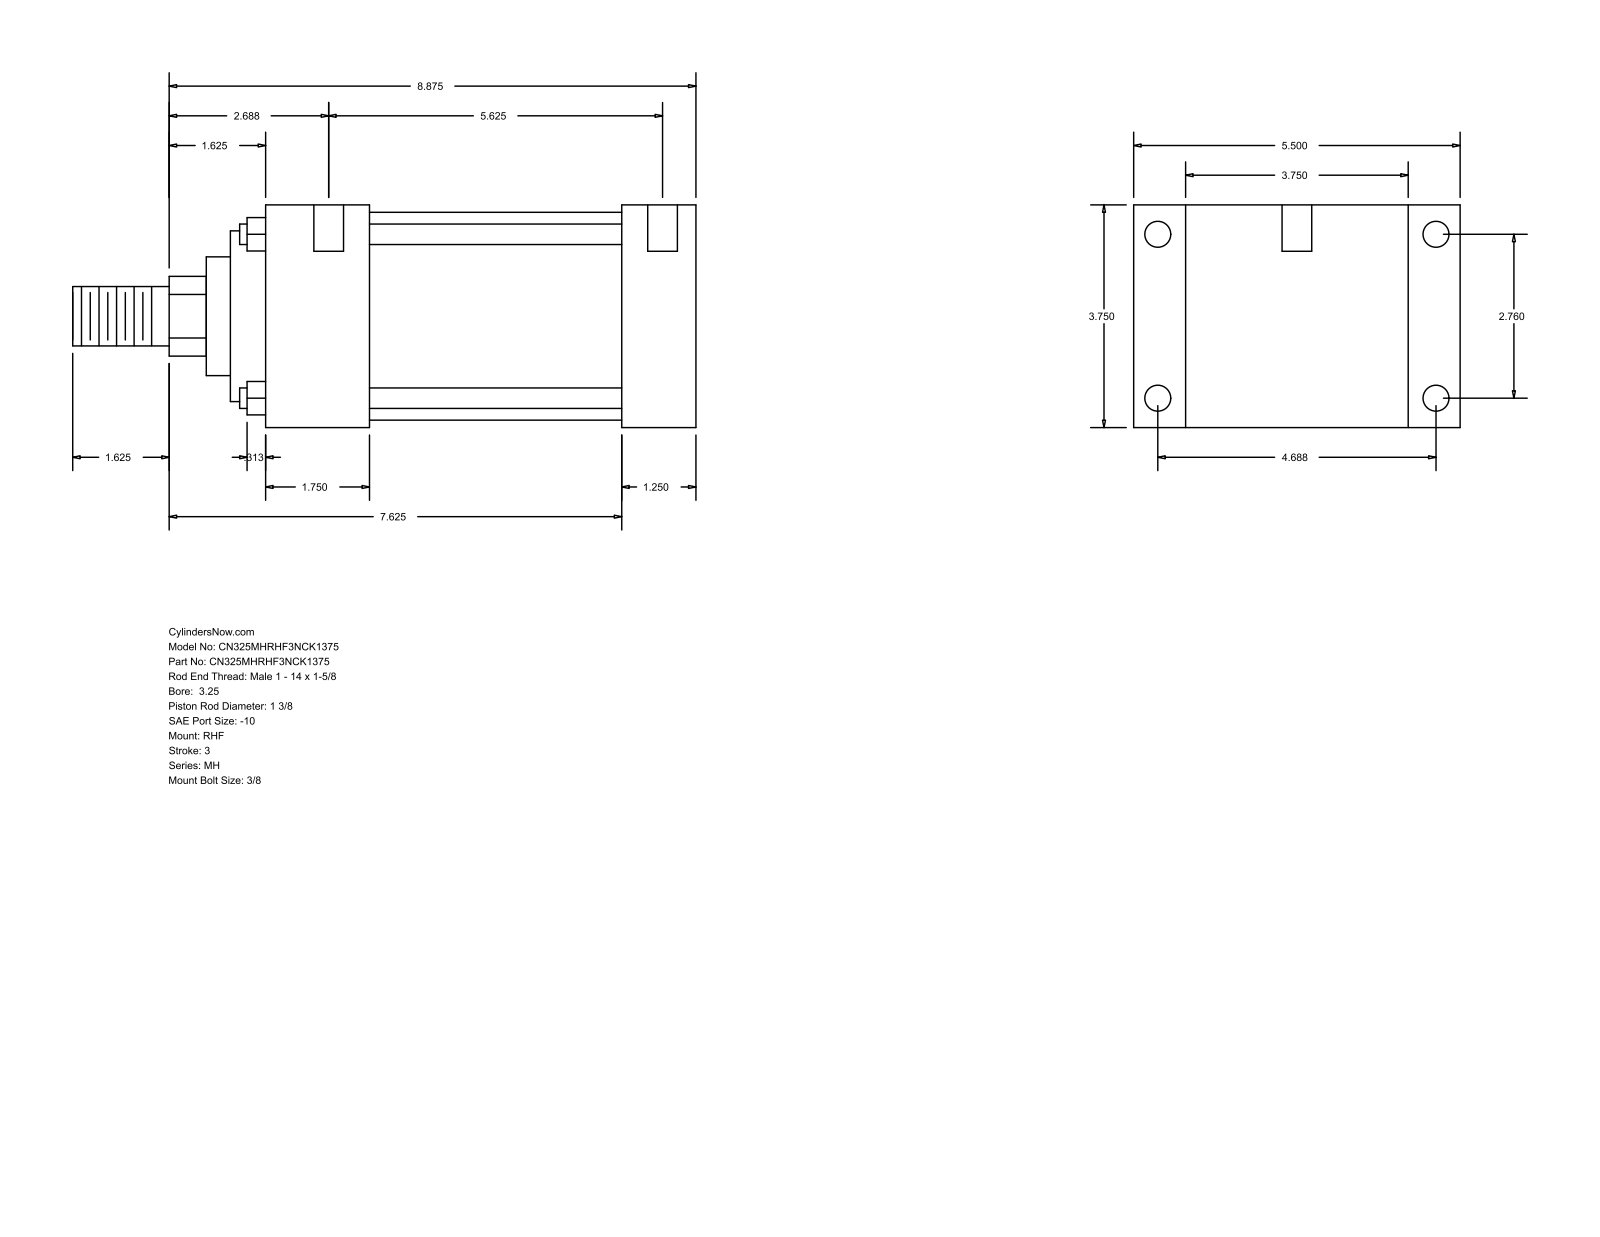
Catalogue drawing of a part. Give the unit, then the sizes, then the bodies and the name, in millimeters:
Units: millimetres
Overall size (bounding box): 266.7 × 139.7 × 95.25
Round holes (diameter × count): ⌀5.56 ×4, ⌀11.13 ×4, ⌀12.7 ×2
Round bosses / shafts (diameter × count): ⌀8.76 ×4, ⌀88.9 ×1, ⌀73.03 ×1, ⌀50.8 ×1, ⌀34.92 ×1, ⌀25.4 ×1
Partial cylindrical surfaces — rounded edges, fillets, slot ends (radius × count): R17.06 ×1
Main face-to-face distances: 95.24, 31.75, 22.23, 117.47, 152.41, 184.16, 139.7, 44.45, 107.96, 139.71
Hole centre spacings: 70.1, 119.06, 138.16, 149.23, 1.59, 4.76, 142.88, 144.47
Bodies: 0 solids, 90 faces (61 planar, 29 cylindrical, 0 other)
Part name (STEP PRODUCT): MH_RHF__0325_1.375
STEP written by: GSSL Pune (CONFIG_CONTROL_DESIGN)
